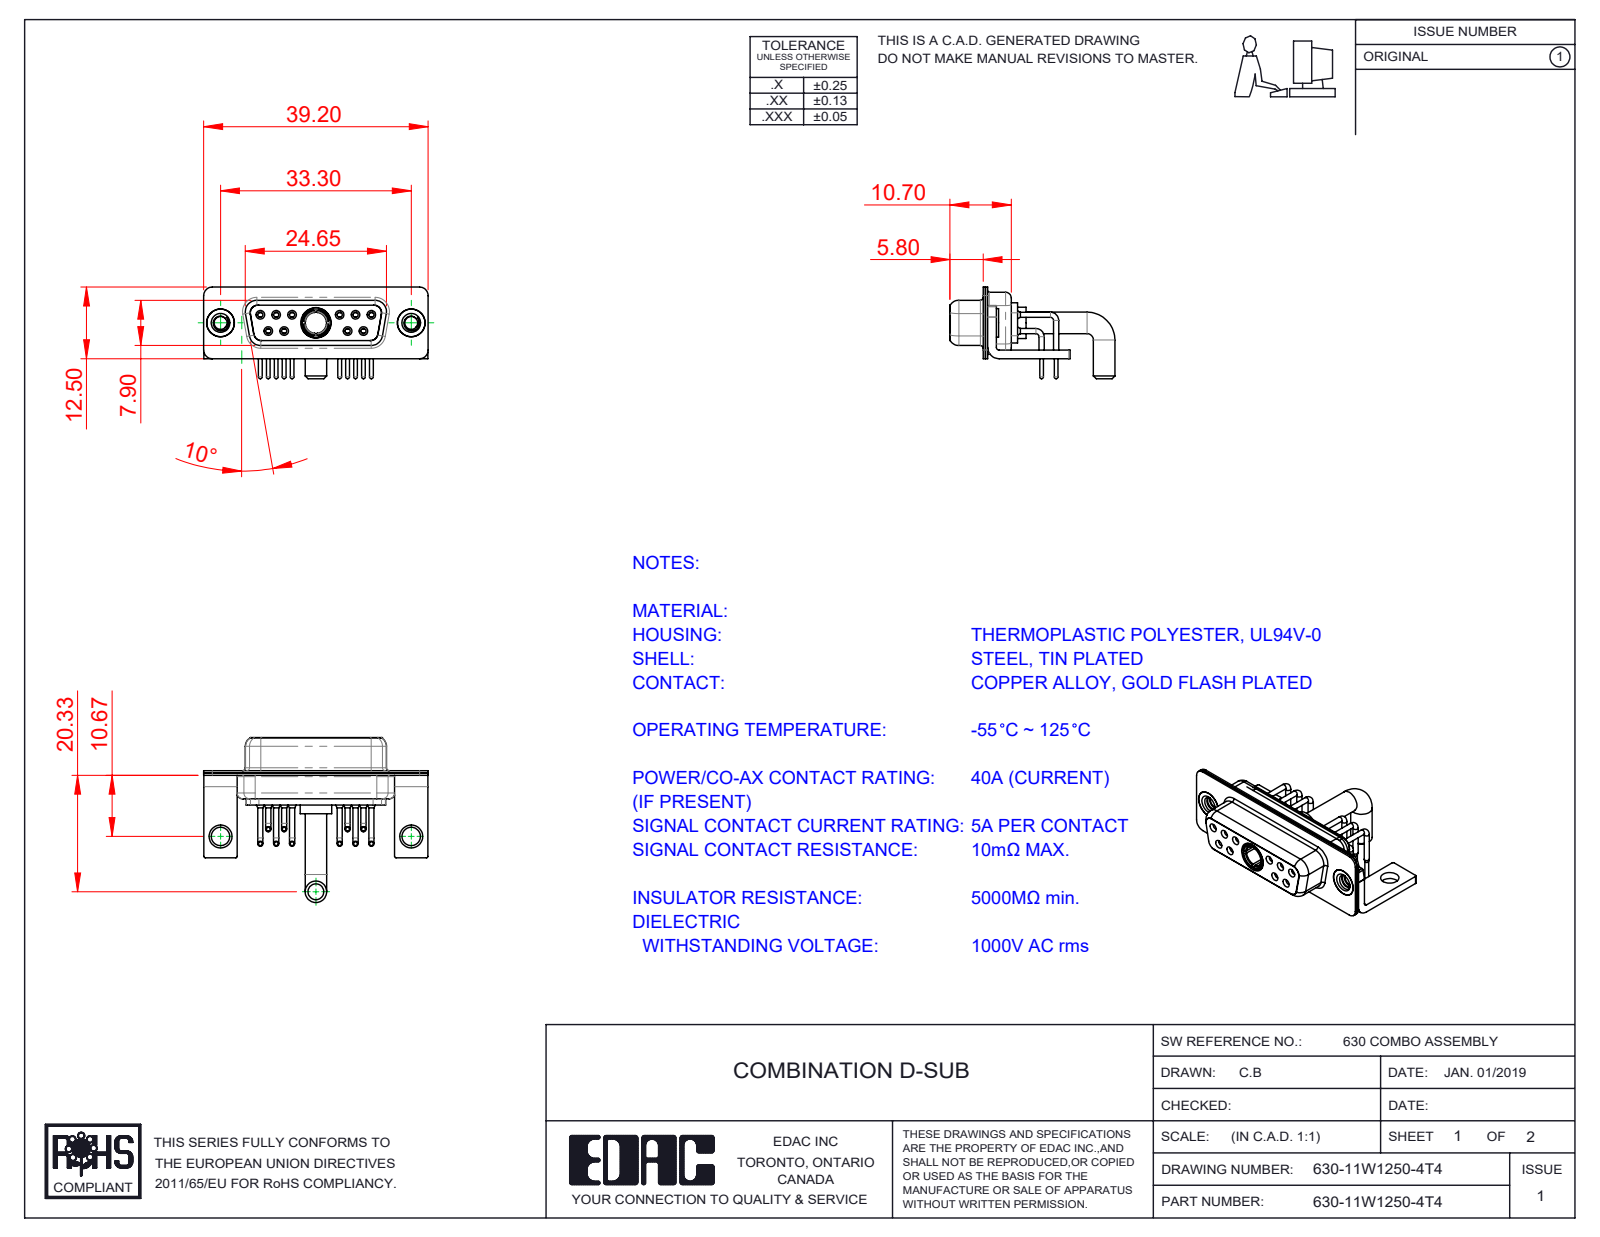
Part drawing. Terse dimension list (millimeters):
name: 630Combo Contact Row 2; Power Socket_Ext 40A RA; 630Combo Shell Rear_15 Contacts; 630Combo Threaded Rivet_3 (+5 more)
written by: SolidWorks 2020 (CONFIG_CONTROL_DESIGN)
unit: mm
bodies: 19 solids, 927 faces (266 planar, 410 cylindrical, 251 other)
size: 39.2 × 28.8 × 16
volume: 3 065 mm³; area: 6 986 mm²
holes: 10× ⌀0.9, 10× ⌀1.1, 10× ⌀1.5, 10× ⌀2, 6× ⌀1.7, 4× ⌀1.6, 3× ⌀4.85, 2× ⌀2.26, 2× ⌀3.2, 2× ⌀4, 2× ⌀4.05, 1× ⌀3.7
bosses: 10× ⌀0.9, 10× ⌀0.65, 6× ⌀1.6, 2× ⌀5, 2× ⌀4.95, 2× ⌀4.8, 2× ⌀3.75, 1× ⌀5.5
rounds: 16× R0.25, 16× R1.5, 13× R2, 12× R1.35, 8× R1.6, 5× R0.5, 4× R0.6, 4× R0.65
face distances: 0.4, 0.8, 1.4, 0.45, 8.45, 1.5, 1.8, 8.9, 6.2, 2.3
hole spacings: 3.16, 2.77, 13.85, 11.08, 16.62, 5.03, 5.04, 5.54
